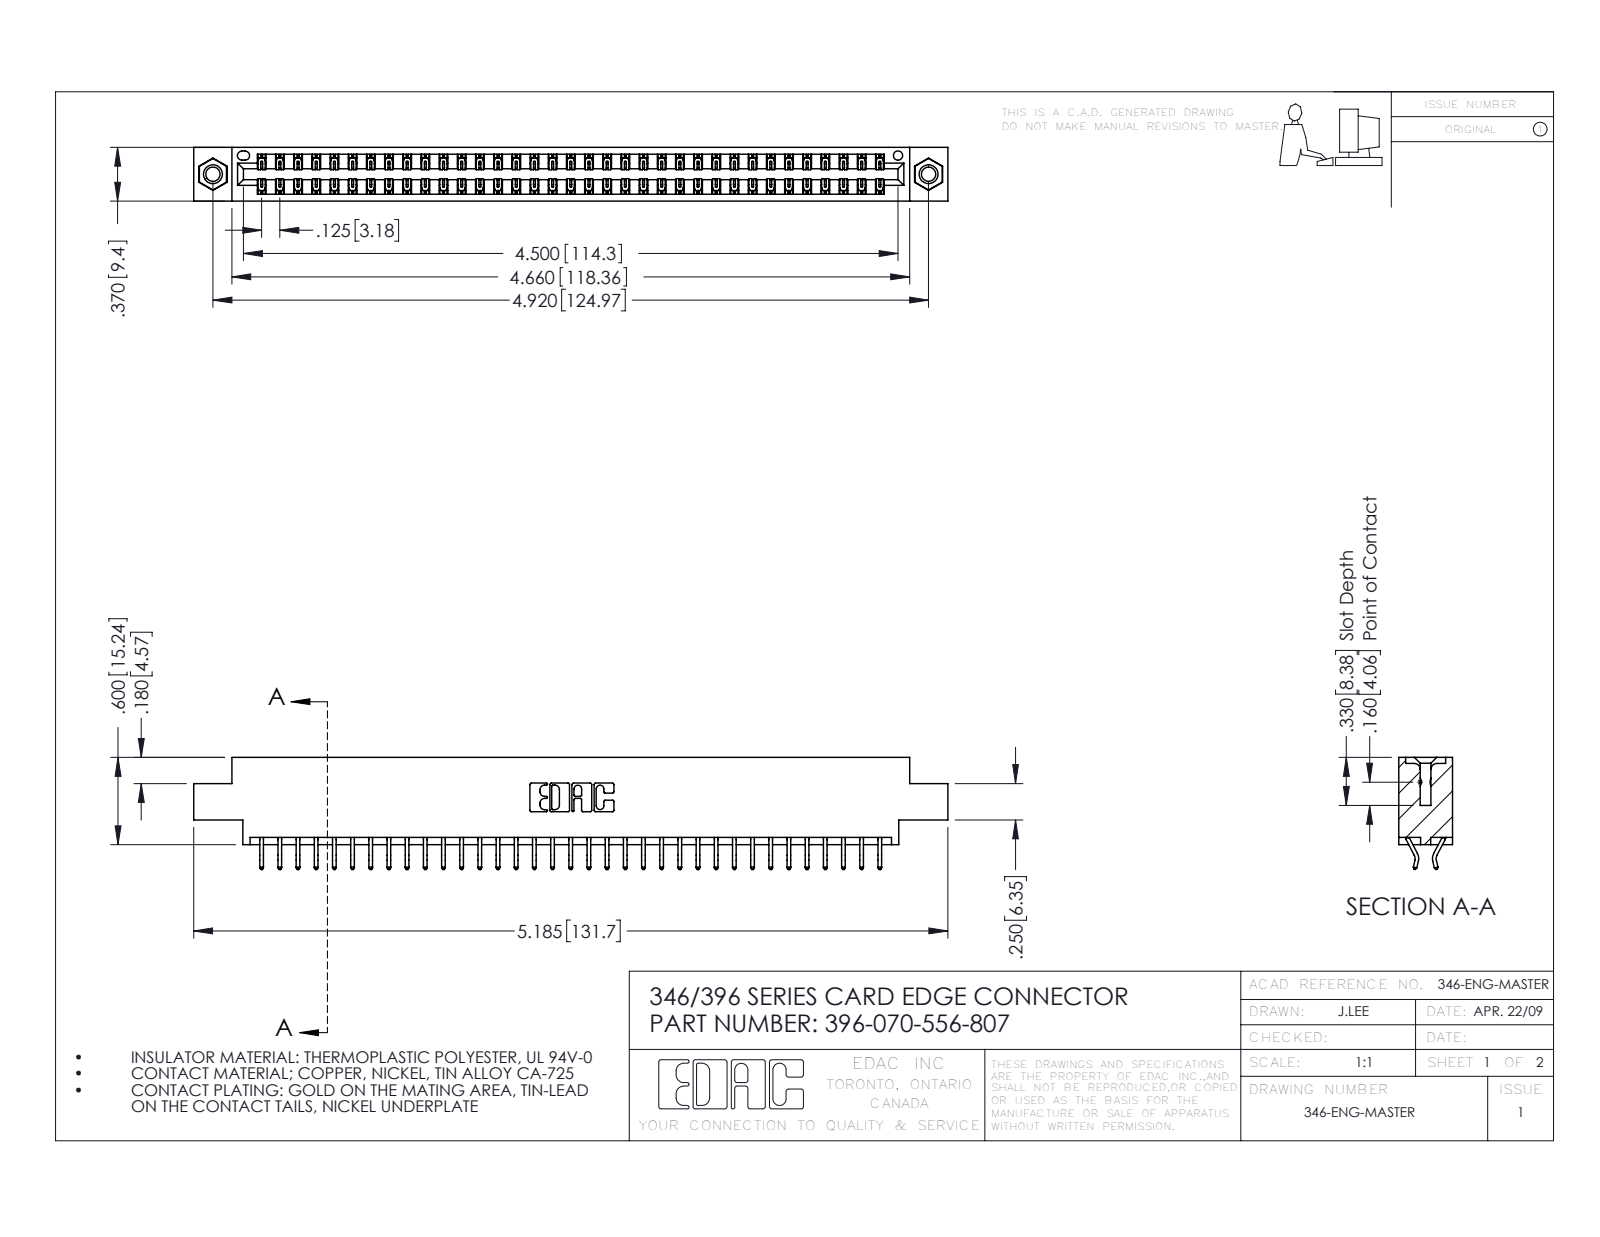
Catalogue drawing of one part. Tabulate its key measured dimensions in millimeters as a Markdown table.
| quantity | value |
| --- | --- |
| part name | 345-250-001_345-250-005-103; 346 Part_0.170 Offset - 0.156 Dia-TI; 396-070-556-807; 345-292-001_556 Tail |
| STEP written by | SolidWorks 2016 (CONFIG_CONTROL_DESIGN) |
| units | millimeters |
| bodies | 73 solids, 4246 faces (2842 planar, 1388 cylindrical, 16 other) |
| overall size | 131.7 × 19.6 × 9.4 |
| volume | 12 600 mm³ |
| surface area | 17 380 mm² |
| round holes (diameter × count) | 2.5 × 2, 3.2 × 2, 4 × 2, 1.6 × 1 |
| round bosses / shafts (diameter × count) | 3.9 × 2 |
| partial cylindrical surfaces (radius × count) | 0.2 × 105, 0.3 × 22, 0.2 × 6, 0.8 × 6, 0.7 × 3, 0.3 × 2, 0.4 × 2, 0.6 × 2 |
| main face-to-face distances | 1.2, 8.2, 9.4, 6.4, 0.6, 1.8, 7.6, 7, 5.6, 3.8 |
| hole center spacings | 6.2, 119.7, 125 |
